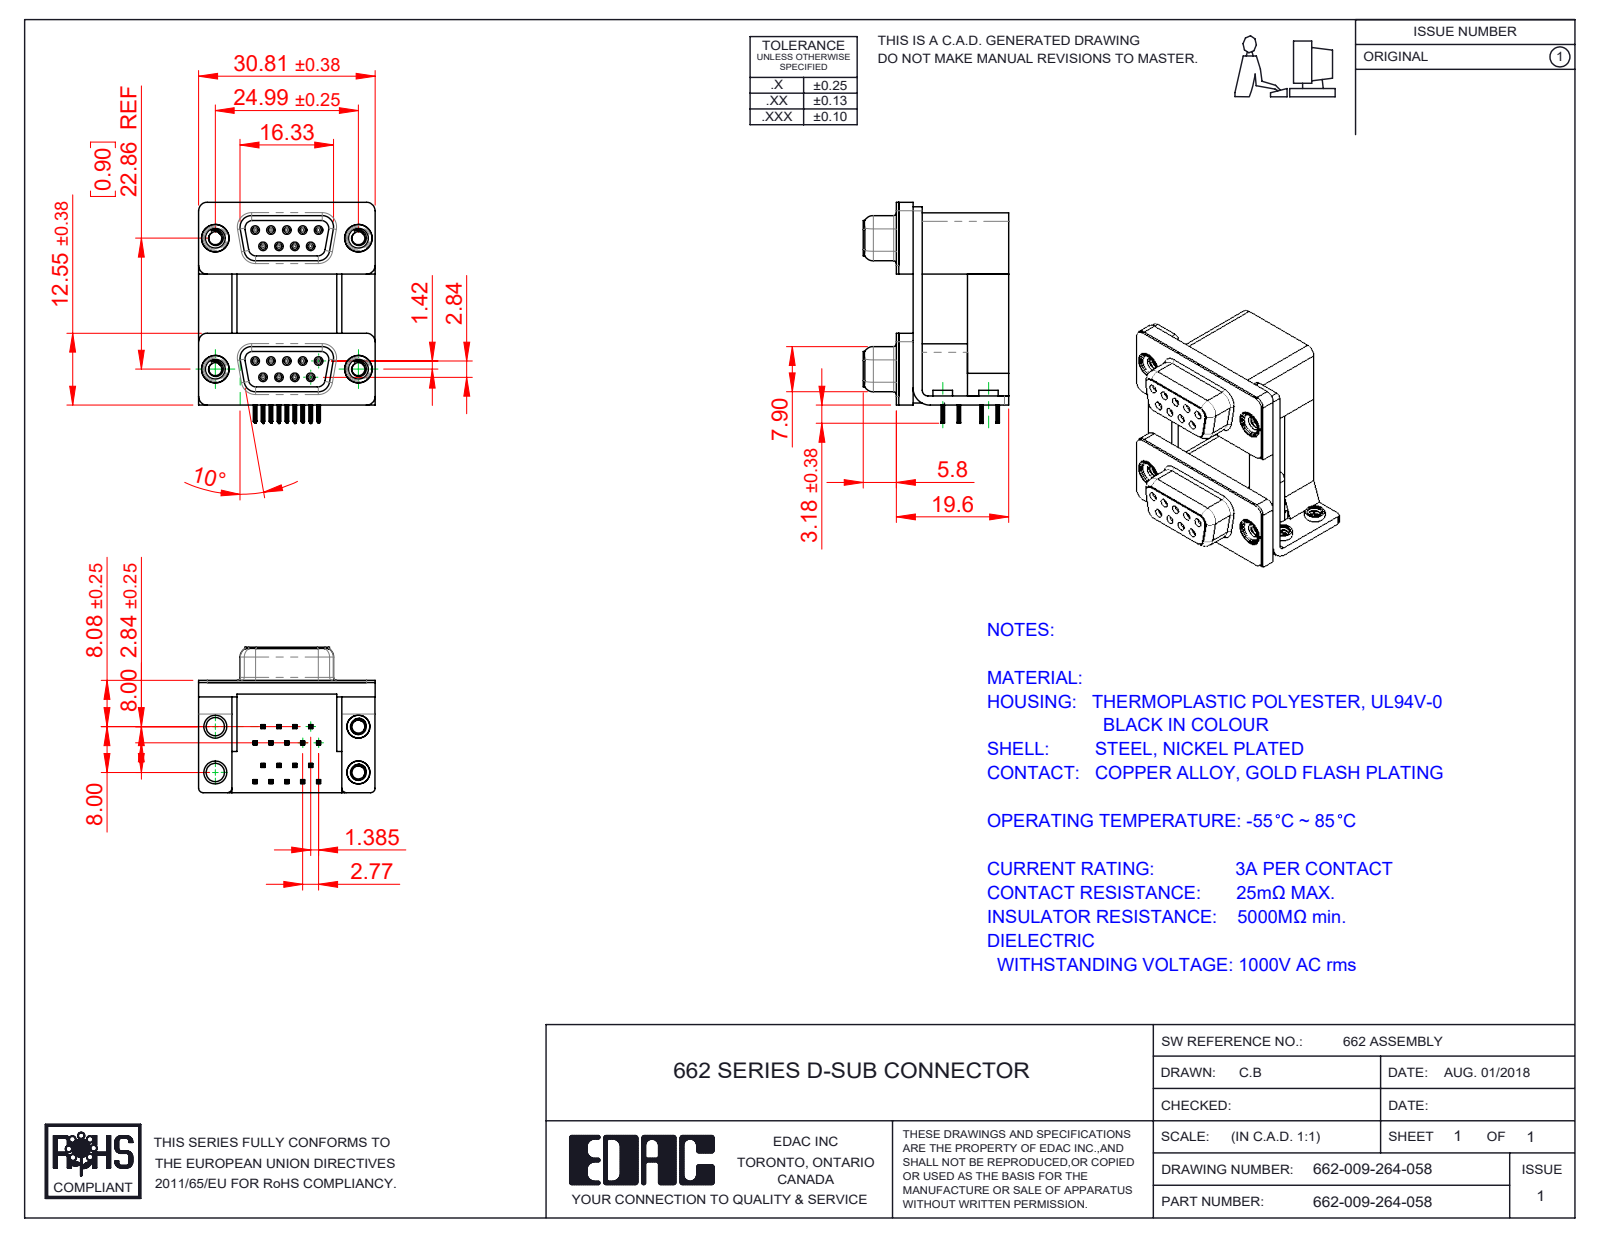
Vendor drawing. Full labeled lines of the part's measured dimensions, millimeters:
Part name (STEP PRODUCT): 662 Contact Top Lower; 662-009-264-058; 662 Contact Top Upper_H; 662 Housing Lower_09 Contacts (+8 more)
STEP written by: SolidWorks 2020 (CONFIG_CONTROL_DESIGN)
Units: millimetres
Bodies: 33 solids, 3250 faces (1386 planar, 872 cylindrical, 992 other)
Overall size (bounding box): 38.59 × 30.81 × 25.4
Volume: 11 877 mm³ · Surface area: 13 977 mm²
Round holes (diameter × count): ⌀0.8 ×18, ⌀0.9 ×18, ⌀2.26 ×8, ⌀2.75 ×4, ⌀3.2 ×4, ⌀3.5 ×4, ⌀4 ×4, ⌀4.8 ×4, ⌀5 ×4
Round bosses / shafts (diameter × count): ⌀1.2 ×18, ⌀4.9 ×4, ⌀4.75 ×4, ⌀4 ×4, ⌀3.9 ×4, ⌀3.4 ×4
Partial cylindrical surfaces — rounded edges, fillets, slot ends (radius × count): R0.1 ×144, R0.15 ×72, R0.35 ×36, R0.34 ×18, R1.35 ×16, R1.5 ×13, R0.28 ×8, R0.5 ×8
Main face-to-face distances: 2.5, 16.7, 19.2, 0.4, 22.86, 9.5, 7.2, 12, 2.9, 1.6
Hole centre spacings: 3.16, 2.77, 23.03, 22.86, 5.54, 23.52, 20.07, 25.74
